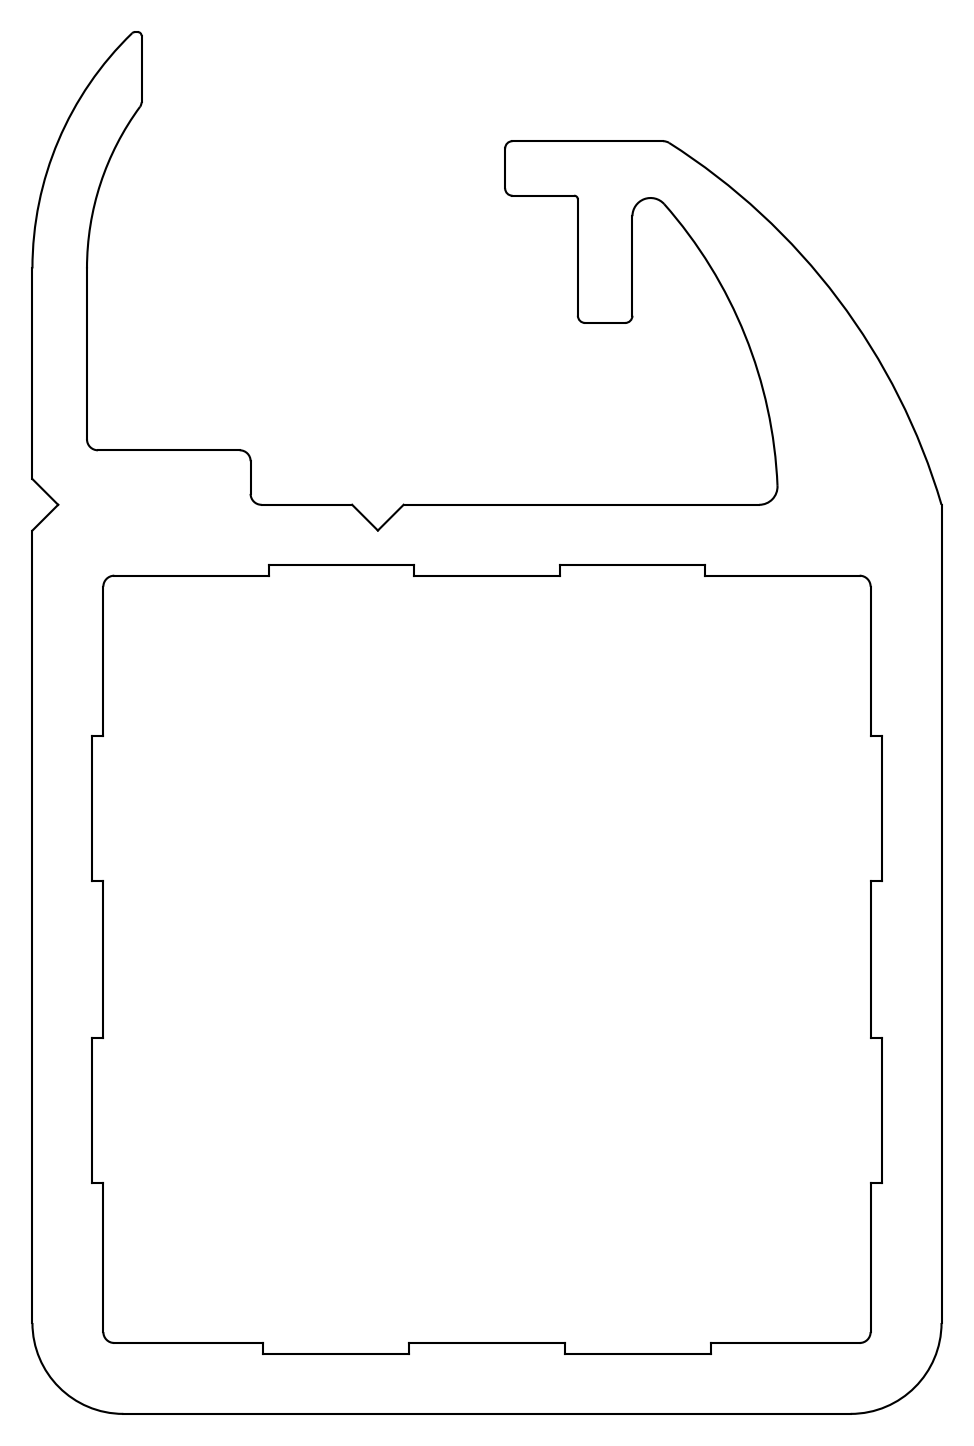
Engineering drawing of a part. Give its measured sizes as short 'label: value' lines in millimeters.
written by: THINKDESIGN (CONFIG_CONTROL_DESIGN)
unit: mm
bodies: 1 solid, 83 faces (59 planar, 24 cylindrical, 0 other)
size: 100 × 38 × 25
volume: 24 727 mm³; area: 25 082 mm²
rounds: 9× R0.2, 4× R0.3, 3× R0.1, 2× R0.5, 2× R2.5, 1× R7.5, 1× R9, 1× R12.5
face distances: 2.1, 22.9, 25, 1.8, 23.2, 21.1, 20.8, 21.4, 1.5, 8.5
